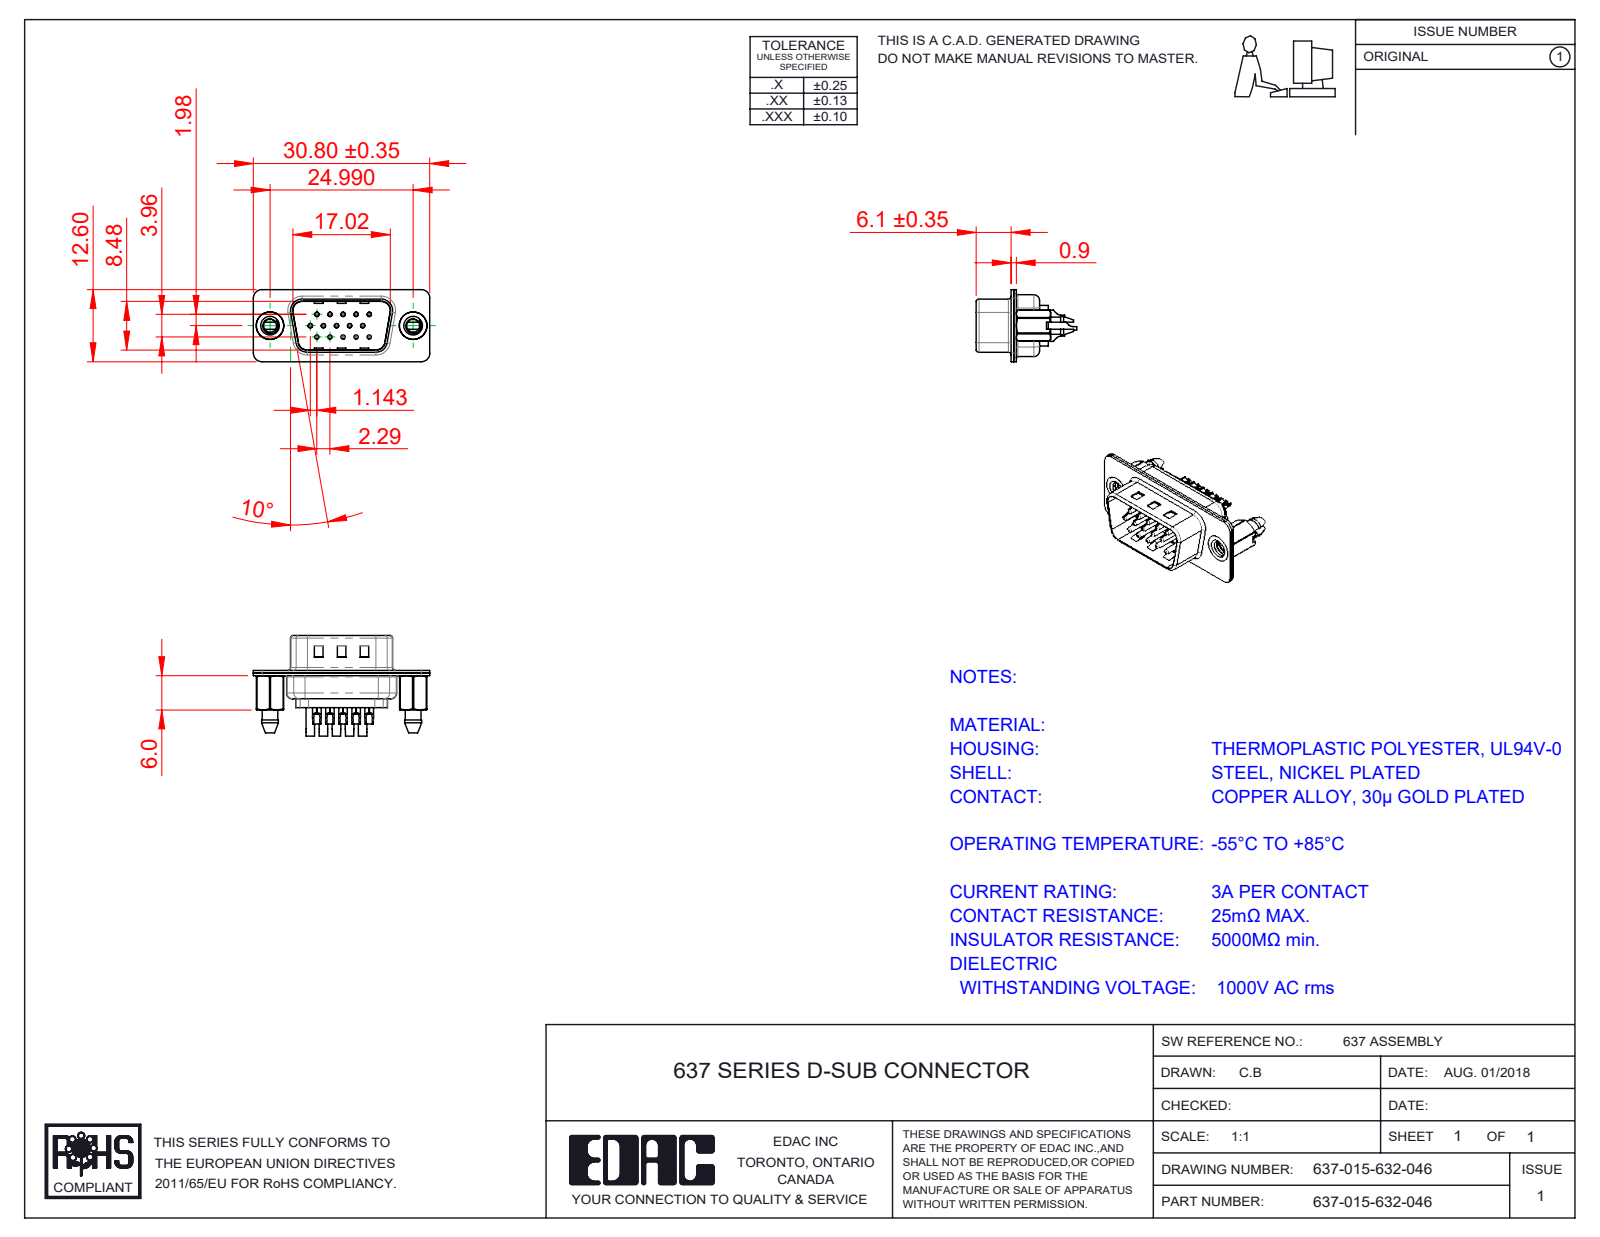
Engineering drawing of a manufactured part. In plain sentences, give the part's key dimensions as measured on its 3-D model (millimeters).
The part is named "637 Shell Front_15 Contacts; 637 Housing_15 Contacts; 637 Shell Rear_15 Contacts; 637 Contact Row 1_32 (+4 more)". Its 3-D file was written by "SolidWorks 2020 (CONFIG_CONTROL_DESIGN)". It is 20 solids with 1338 faces: 349 planar, 596 cylindrical and 393 other. Overall it measures 30.8 by 17.55 by 12.6 millimeters. Its volume is 1 444 cubic millimeters and its surface area 5 064 square millimeters. Round holes: 15 of diameter 0.35, 15 of diameter 1.1, 15 of diameter 1.6, 2 of diameter 2.26, 2 of diameter 4, 2 of diameter 4.8. Round bosses or shafts: 15 of diameter 2, 15 of diameter 1.5, 15 of diameter 0.75, 2 of diameter 4.9. Partial cylindrical surfaces (rounded edges, fillets, slot ends): 18 of radius 1.5, 12 of radius 2, 8 of radius 0.5, 7 of radius 1, 6 of radius 1.6, 4 of radius 0.25, 4 of radius 0.55, 4 of radius 0.7. The main face-to-face distances are 0.45, 0.4, 0.9, 0.7, 8.88, 8.48, 6.5, 1.05, 4.55, 0.31. The hole center spacings are 3.96, 2.28, 4.57, 2.29, 6.05, 6.86, 7.92, 6.04.
